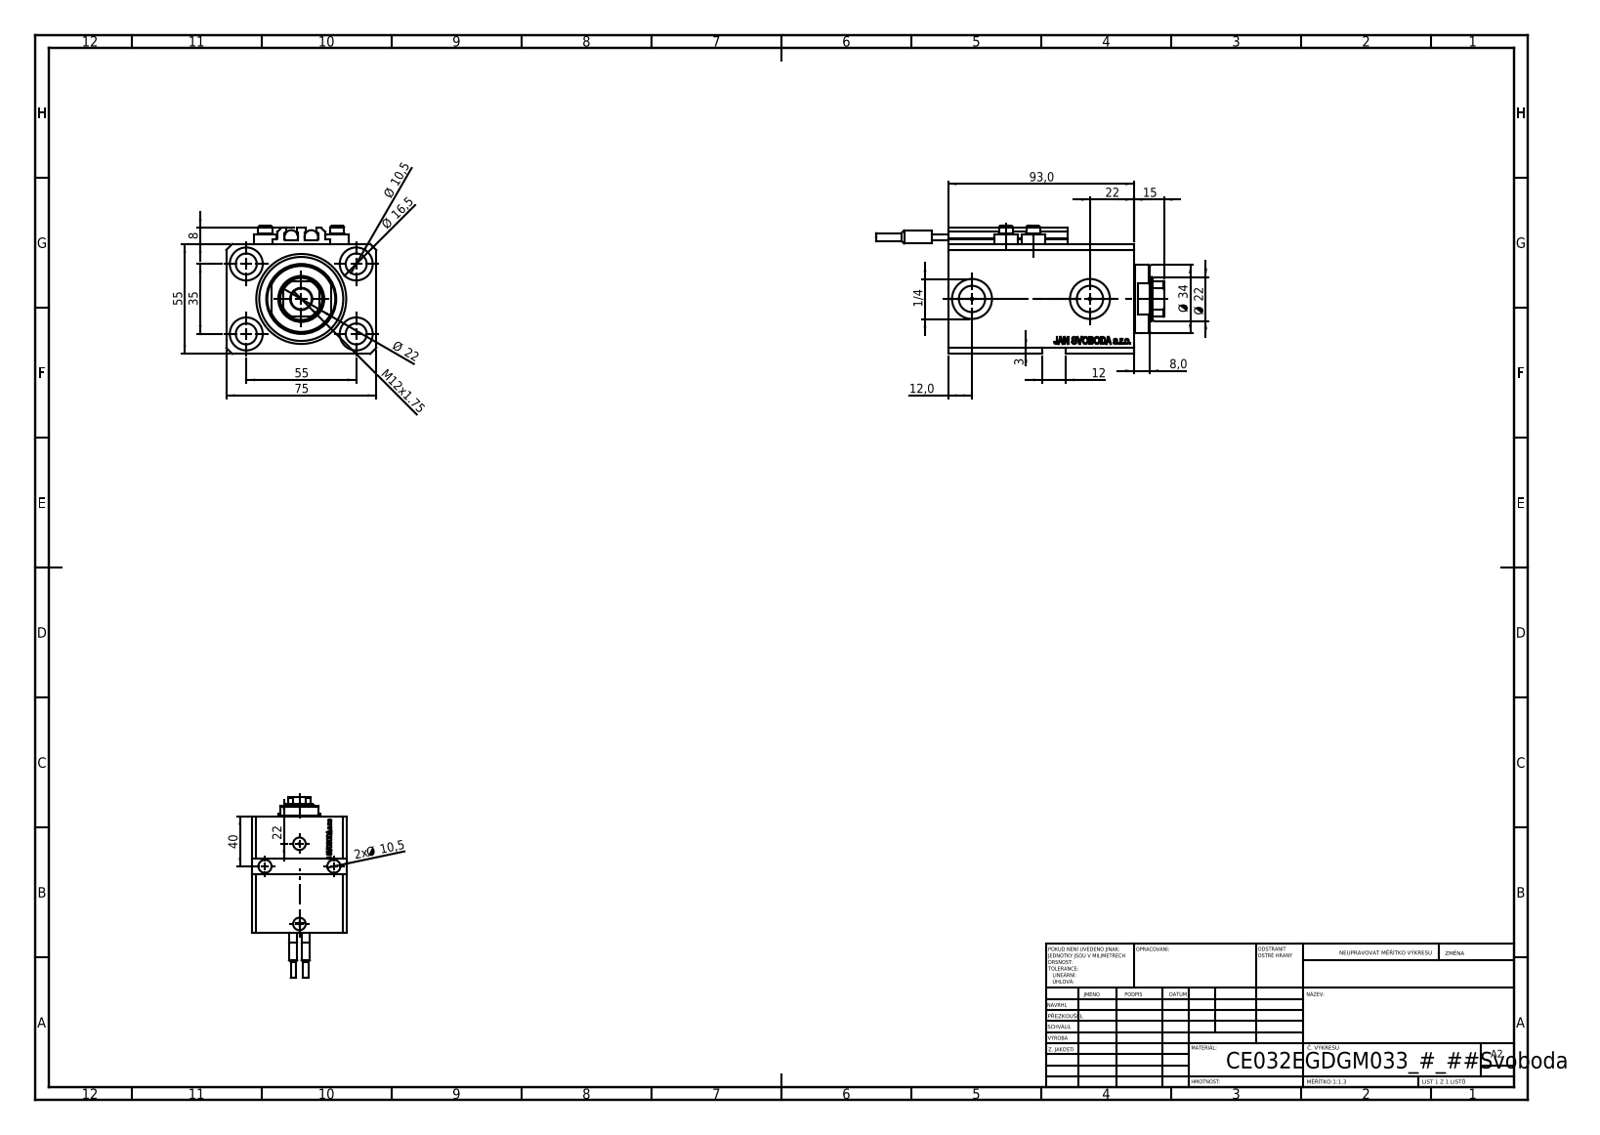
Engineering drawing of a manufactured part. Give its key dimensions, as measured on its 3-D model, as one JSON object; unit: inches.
{"part_name": "V250CE_C_VCP; ALLEN BOLT V250CE; V250CE_E_Body; SWITCH_V250CE (+1 more)", "step_written_by": "SolidWorks 2019 (CONFIG_CONTROL_DESIGN)", "units": "inches", "bodies": {"solids": 10, "faces": 1132, "planar": 550, "cylindrical": 150, "other": 432}, "overall_size": [5.669, 2.953, 2.52], "volume_in3": 20.07, "surface_area_in2": 134.7, "round_holes": [[0.413, 7], [0.049, 4], [0.157, 4], [0.65, 4], [0.394, 2], [0.518, 2], [0.787, 2], [0.866, 1], [1.26, 1], [1.772, 1]], "round_bosses_or_shafts": [[0.457, 4], [0.276, 4], [0.268, 2], [0.256, 2], [0.157, 2], [1.339, 1]], "partial_cylinders_radius": [[0.008, 10], [0.413, 1]], "face_to_face_distances": [2.165, 2.953, 0.591, 0.118, 3.661, 3.071, 0.39, 2.244, 2.681, 3.272], "hole_center_spacings": [1.283, 2.165, 0.535, 0.555, 1.016, 1.103, 1.119, 1.294]}
